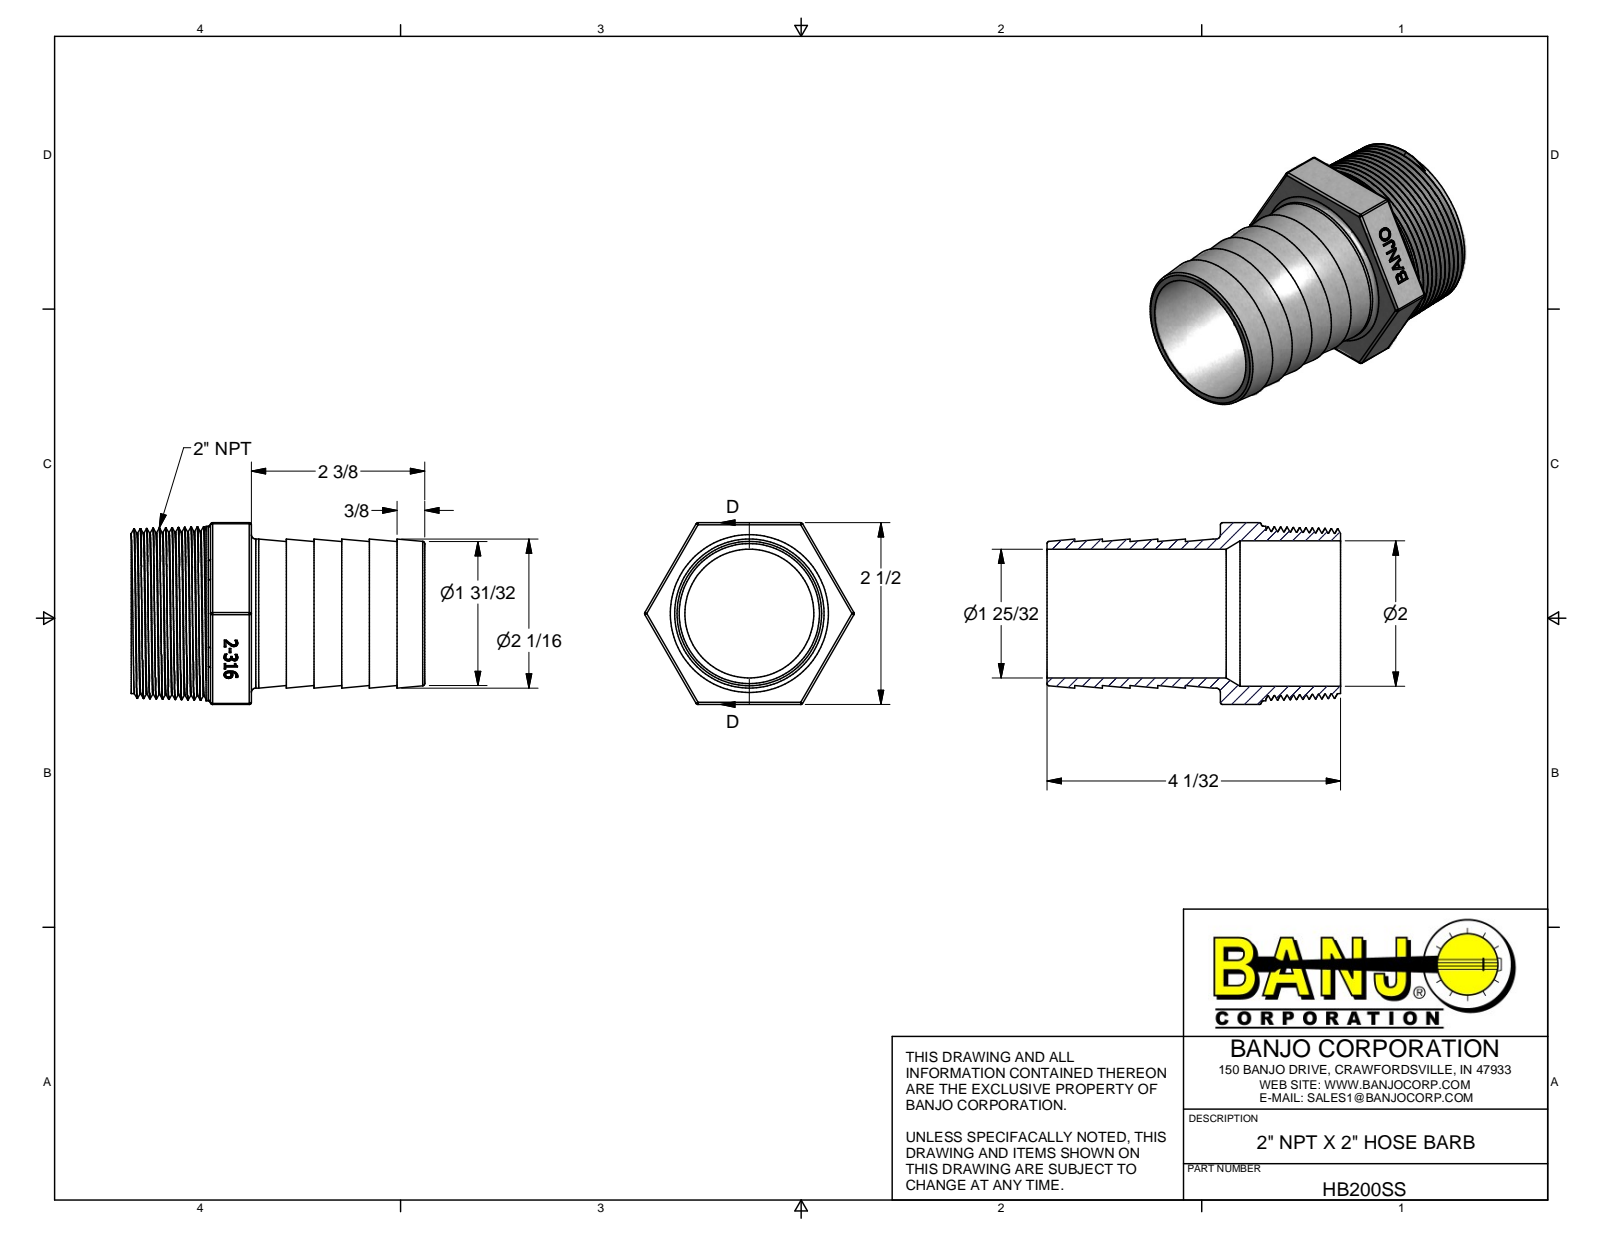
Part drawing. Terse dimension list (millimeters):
name: HB200SS
written by: Autodesk Inventor 2014 (AUTOMOTIVE_DESIGN)
unit: mm
bodies: 1 solid, 244 faces (102 planar, 23 cylindrical, 119 other)
size: 102.36 × 73.09 × 63.5
volume: 69 376 mm³; area: 40 486 mm²
holes: 1× ⌀44.96, 1× ⌀50.8
bosses: 1× ⌀60.96, 1× ⌀52.07
rounds: 18× R0.76, 1× R15.6
face distances: 63.5, 9.65, 28.96, 41.91, 60.45, 102.36, 19.3, 38.61, 19.31, 74.74
